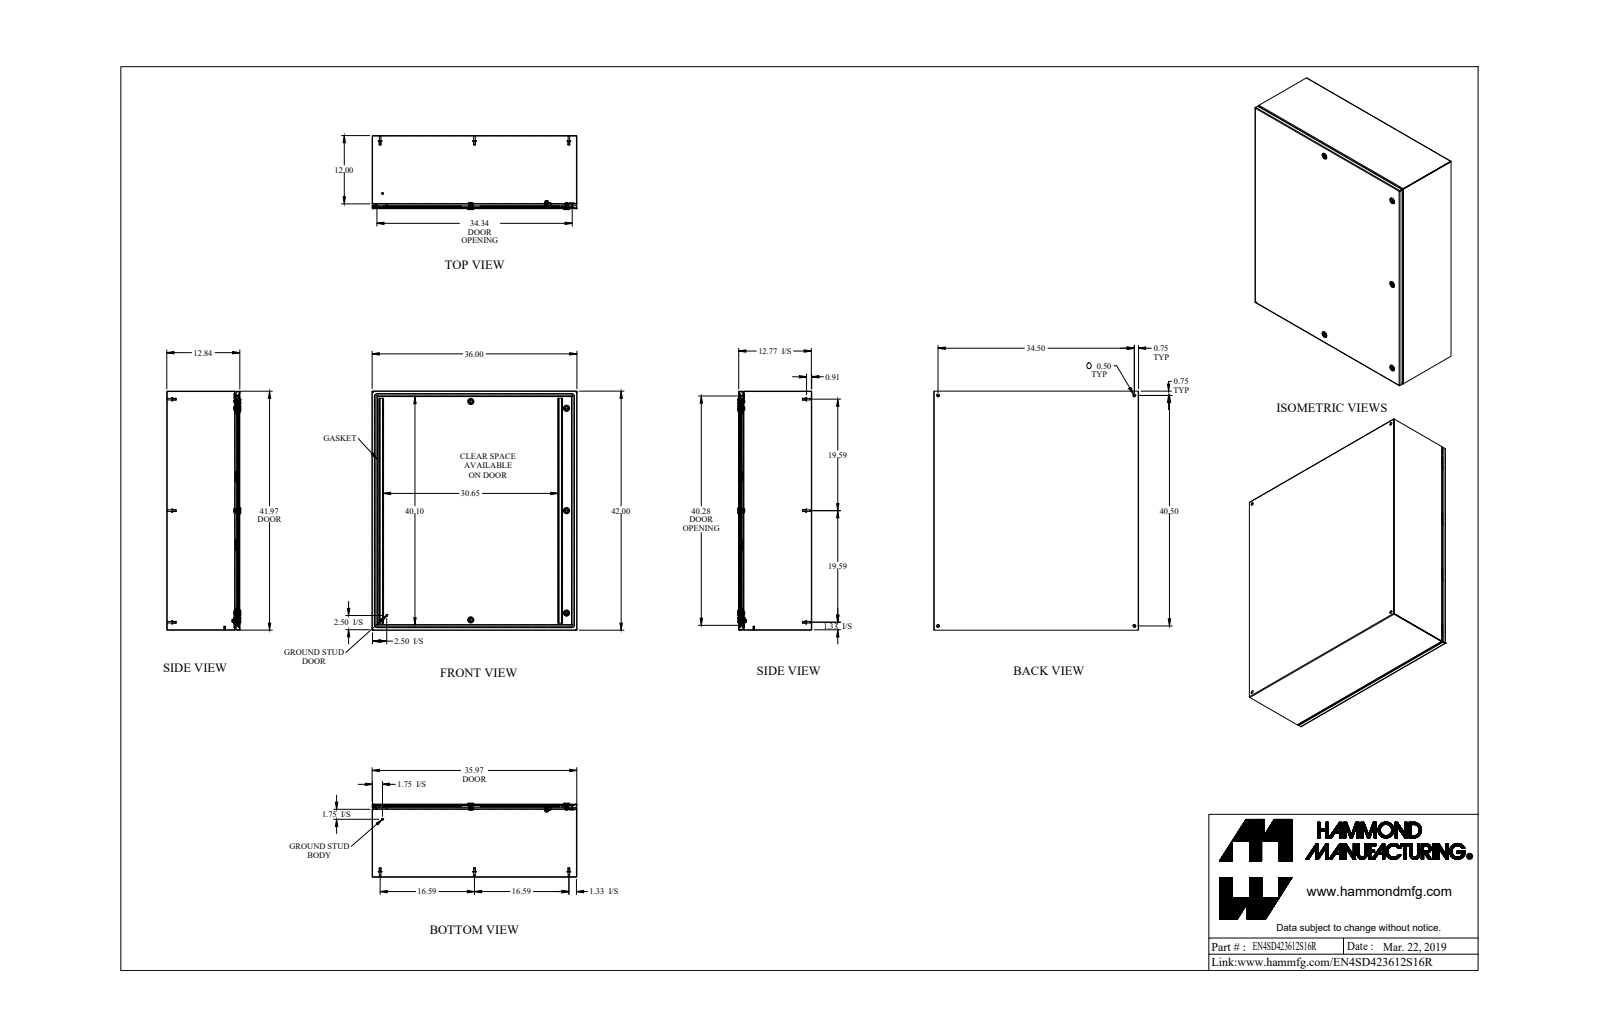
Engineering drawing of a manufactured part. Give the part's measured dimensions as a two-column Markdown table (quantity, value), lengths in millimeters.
| quantity | value |
| --- | --- |
| part name | EN4SD423612S16R |
| STEP written by | SolidWorks 2018 (AUTOMOTIVE_DESIGN) |
| units | millimeters |
| bodies | 66 solids, 1714 faces (896 planar, 545 cylindrical, 273 other) |
| overall size | 1066.8 × 914.4 × 330.2 |
| volume | 6 611 000 mm³ |
| surface area | 7 335 000 mm² |
| round holes (diameter × count) | 12.7 × 9, 5 × 5, 9.8 × 5, 16 × 5, 19.5 × 5, 4.4 × 1, 5 × 1, 6.1 × 1, 6.1 × 1, 7 × 1, 9.5 × 1 |
| round bosses / shafts (diameter × count) | 8 × 10, 15.9 × 9, 7 × 8, 27.9 × 5, 19.9 × 5, 15.9 × 5, 13.3 × 5, 6 × 5 |
| partial cylindrical surfaces (radius × count) | 1.2 × 32, 0.3 × 24, 0.9 × 18, 2.7 × 18, 1.6 × 14, 2.4 × 10, 3.2 × 10, 0.4 × 9 |
| main face-to-face distances | 1.8, 324.3, 322.5, 326.2, 912.6, 1065, 910.7, 914.4, 1063.1, 1066.8 |
| hole center spacings | 422.2, 428.8, 455.8, 515.1, 648.4, 851, 876.3, 992.7 |
